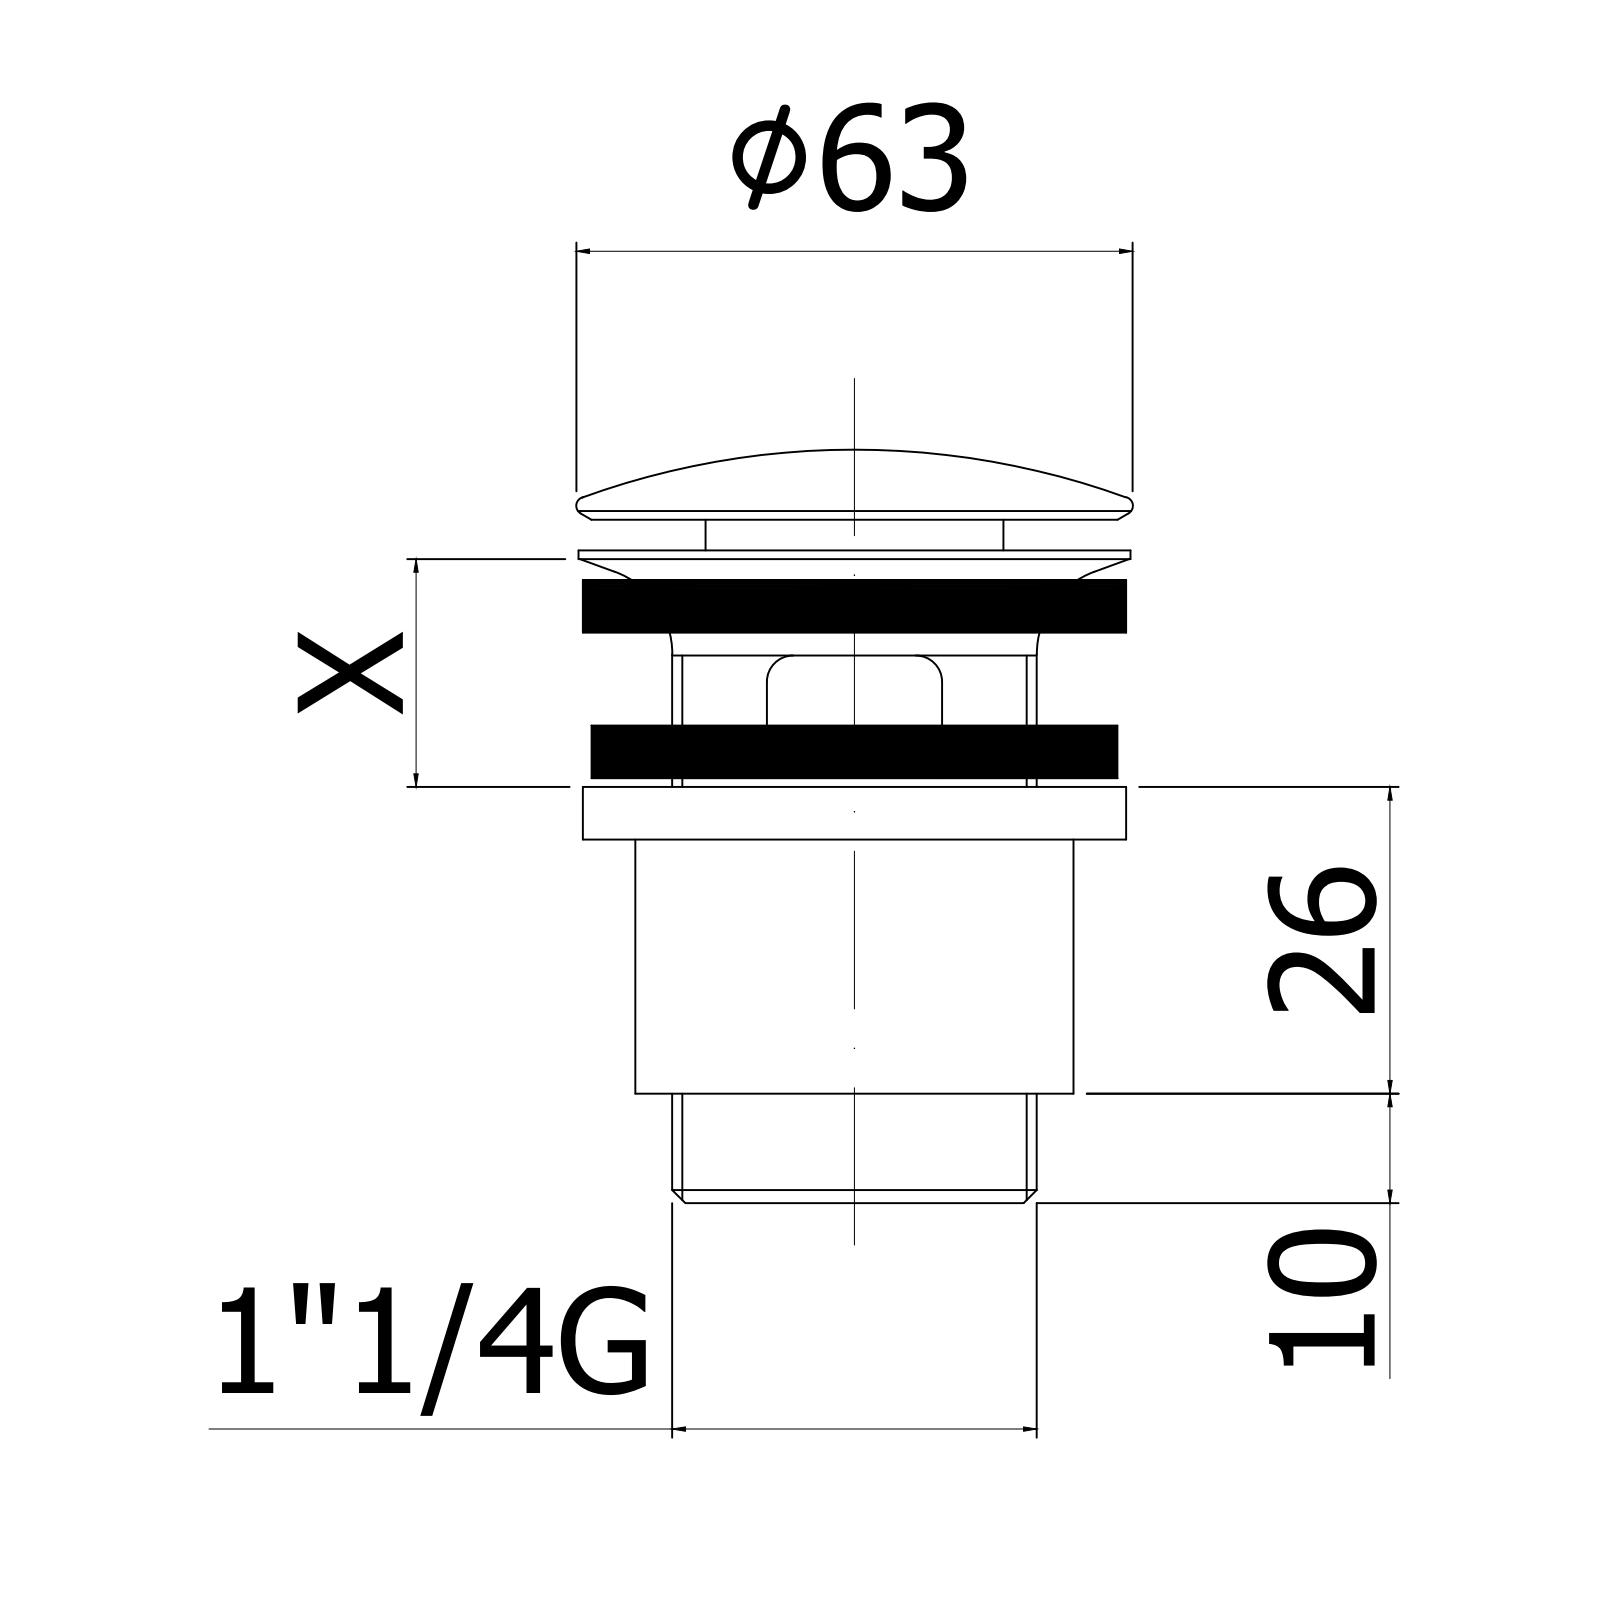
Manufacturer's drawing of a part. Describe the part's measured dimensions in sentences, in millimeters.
The part is named "ZSCA060CR". Its 3-D file was written by "CREO PARAMETRIC BY PTC INC, 2020044 (CONFIG_CONTROL_DESIGN)". It is 1 solid with 540 faces: 215 planar, 169 cylindrical and 156 other. Overall it measures 100.4 by 63 by 63 millimeters. Its volume is 69 661 cubic millimeters and its surface area 57 289 square millimeters. Round holes: 1 of diameter 11.89, 1 of diameter 15.4, 1 of diameter 17.7, 1 of diameter 22, 1 of diameter 24.3, 1 of diameter 30, 1 of diameter 30.5, 1 of diameter 32.4, 1 of diameter 34.5, 1 of diameter 35.6, 1 of diameter 37, 1 of diameter 39.27. Round bosses or shafts: 1 of diameter 63, 1 of diameter 61, 1 of diameter 60, 1 of diameter 48.8, 1 of diameter 43.4, 1 of diameter 39, 1 of diameter 34, 1 of diameter 32. Partial cylindrical surfaces (rounded edges, fillets, slot ends): 16 of radius 2, 12 of radius 1, 2 of radius 0.2, 2 of radius 2, 1 of radius 4.25, 1 of radius 8, 1 of radius 8.7, 1 of radius 13.05. The main face-to-face distances are 37.25, 4.5, 6.5, 22.95, 60.2, 10, 51.1, 81.2, 47.1, 24.15.
